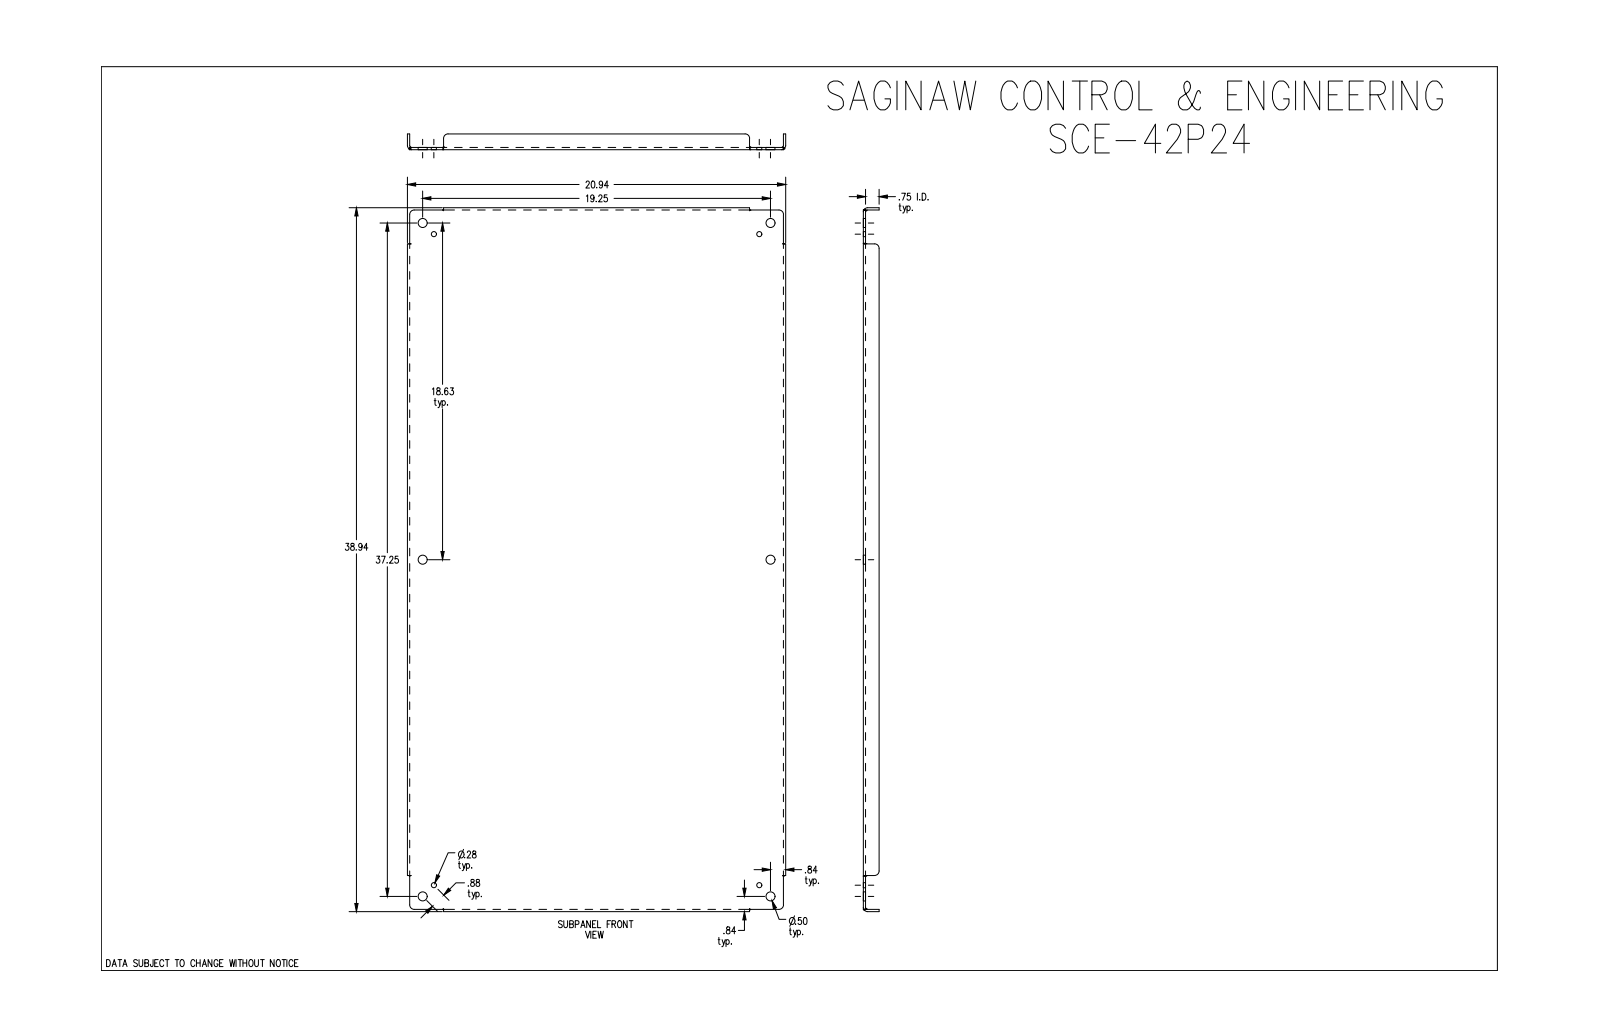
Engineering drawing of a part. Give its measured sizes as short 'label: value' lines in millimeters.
name: SCE-42P24
written by: SolidWorks 2019 (CONFIG_CONTROL_DESIGN)
unit: mm
bodies: 1 solid, 84 faces (30 planar, 30 cylindrical, 24 other)
size: 989 × 531.8 × 22.2
volume: 1 806 000 mm³; area: 1 149 000 mm²
holes: 6× ⌀12.7, 4× ⌀7.1
rounds: 8× R6.4, 4× R2.8, 4× R6
face distances: 3.2, 3.2, 528.7, 525.4, 531.8, 985.9, 19.1, 22.2, 982.6, 989
hole spacings: 22.2, 457.6, 473.1, 473.5, 658.1, 680.3, 930.6, 1043.9
